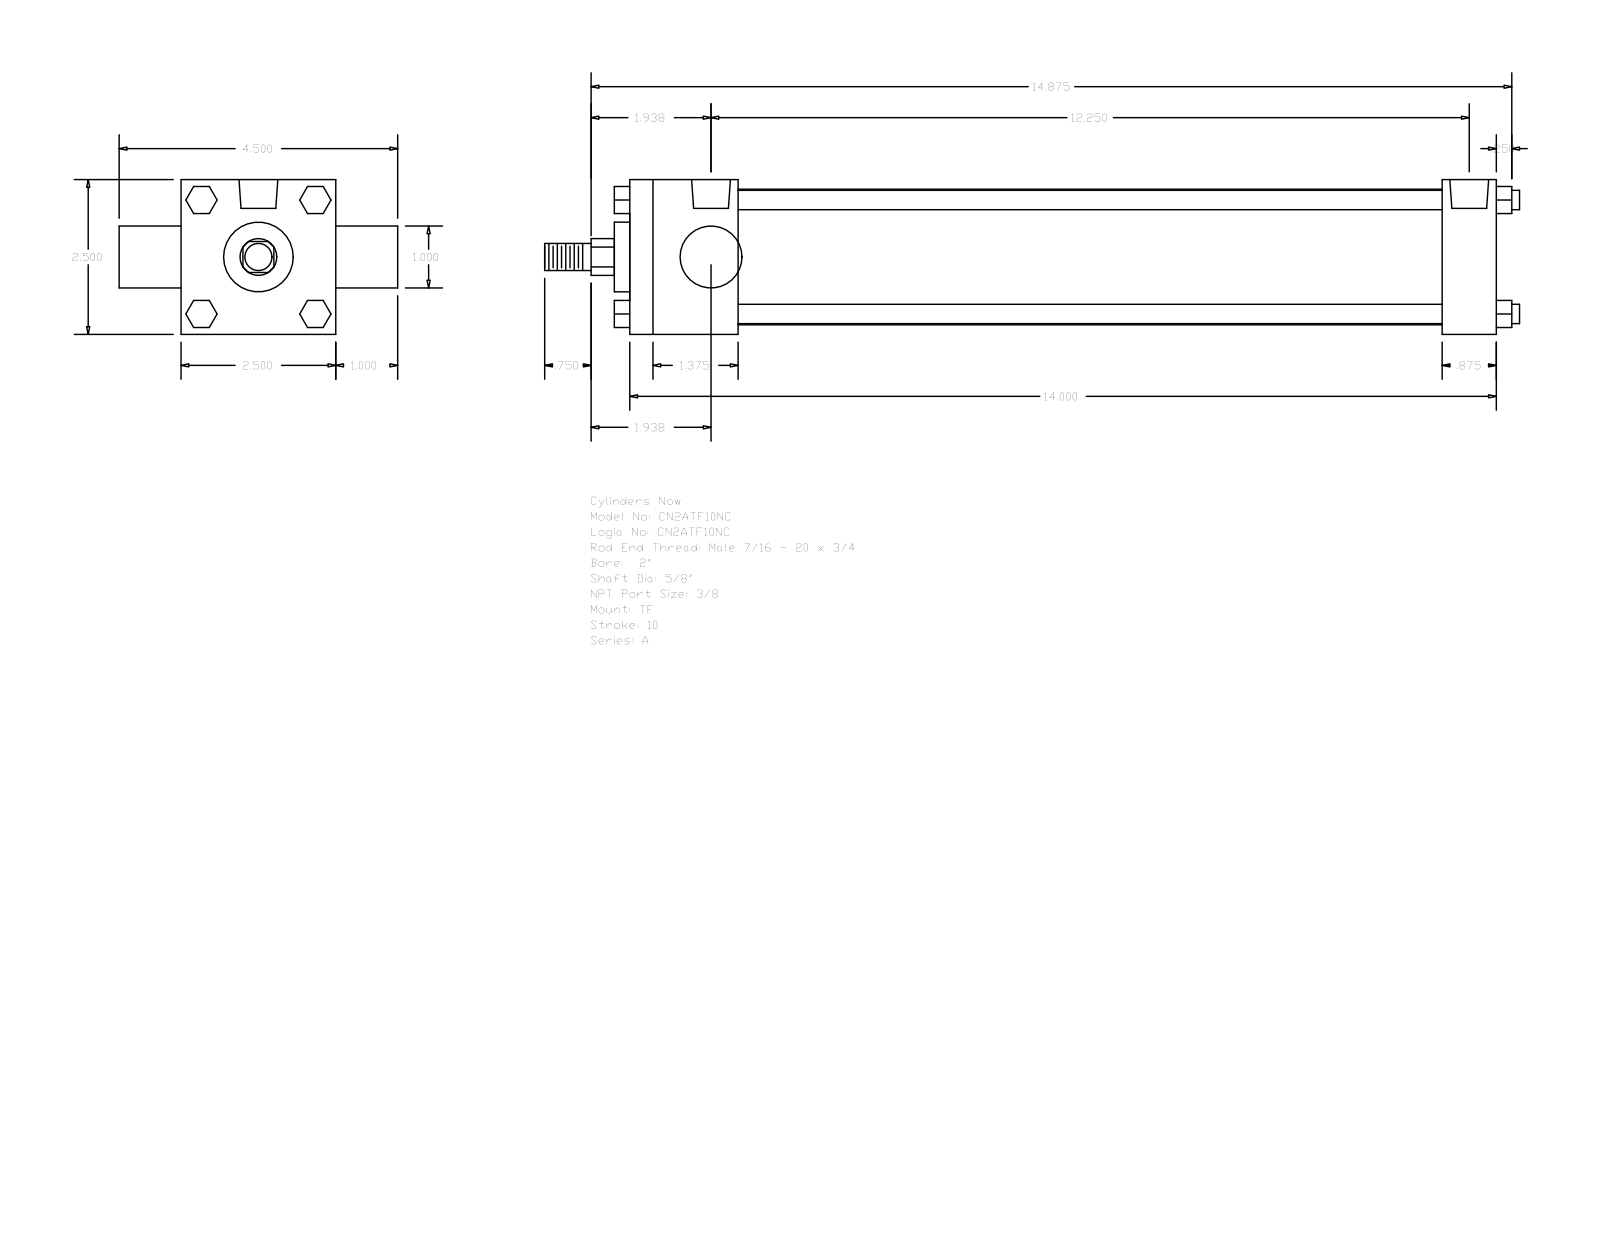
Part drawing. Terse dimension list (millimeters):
name: A_TF__0200_0.625
written by: GSSL Pune (CONFIG_CONTROL_DESIGN)
unit: mm
bodies: 0 solids, 120 faces (92 planar, 28 cylindrical, 0 other)
size: 400.05 × 114.3 × 63.5
holes: 3× ⌀5.56, 2× ⌀15.93
bosses: 4× ⌀7.94, 1× ⌀55.63, 1× ⌀28.57, 1× ⌀25.4, 1× ⌀15.88, 1× ⌀11.11
rounds: 1× R7.54
face distances: 63.5, 355.6, 44.45, 333.37, 288.92, 311.15, 22.23, 25.4, 88.9, 50.8
hole spacings: 3.97, 3.98, 303.2, 307.17, 307.18, 311.15
